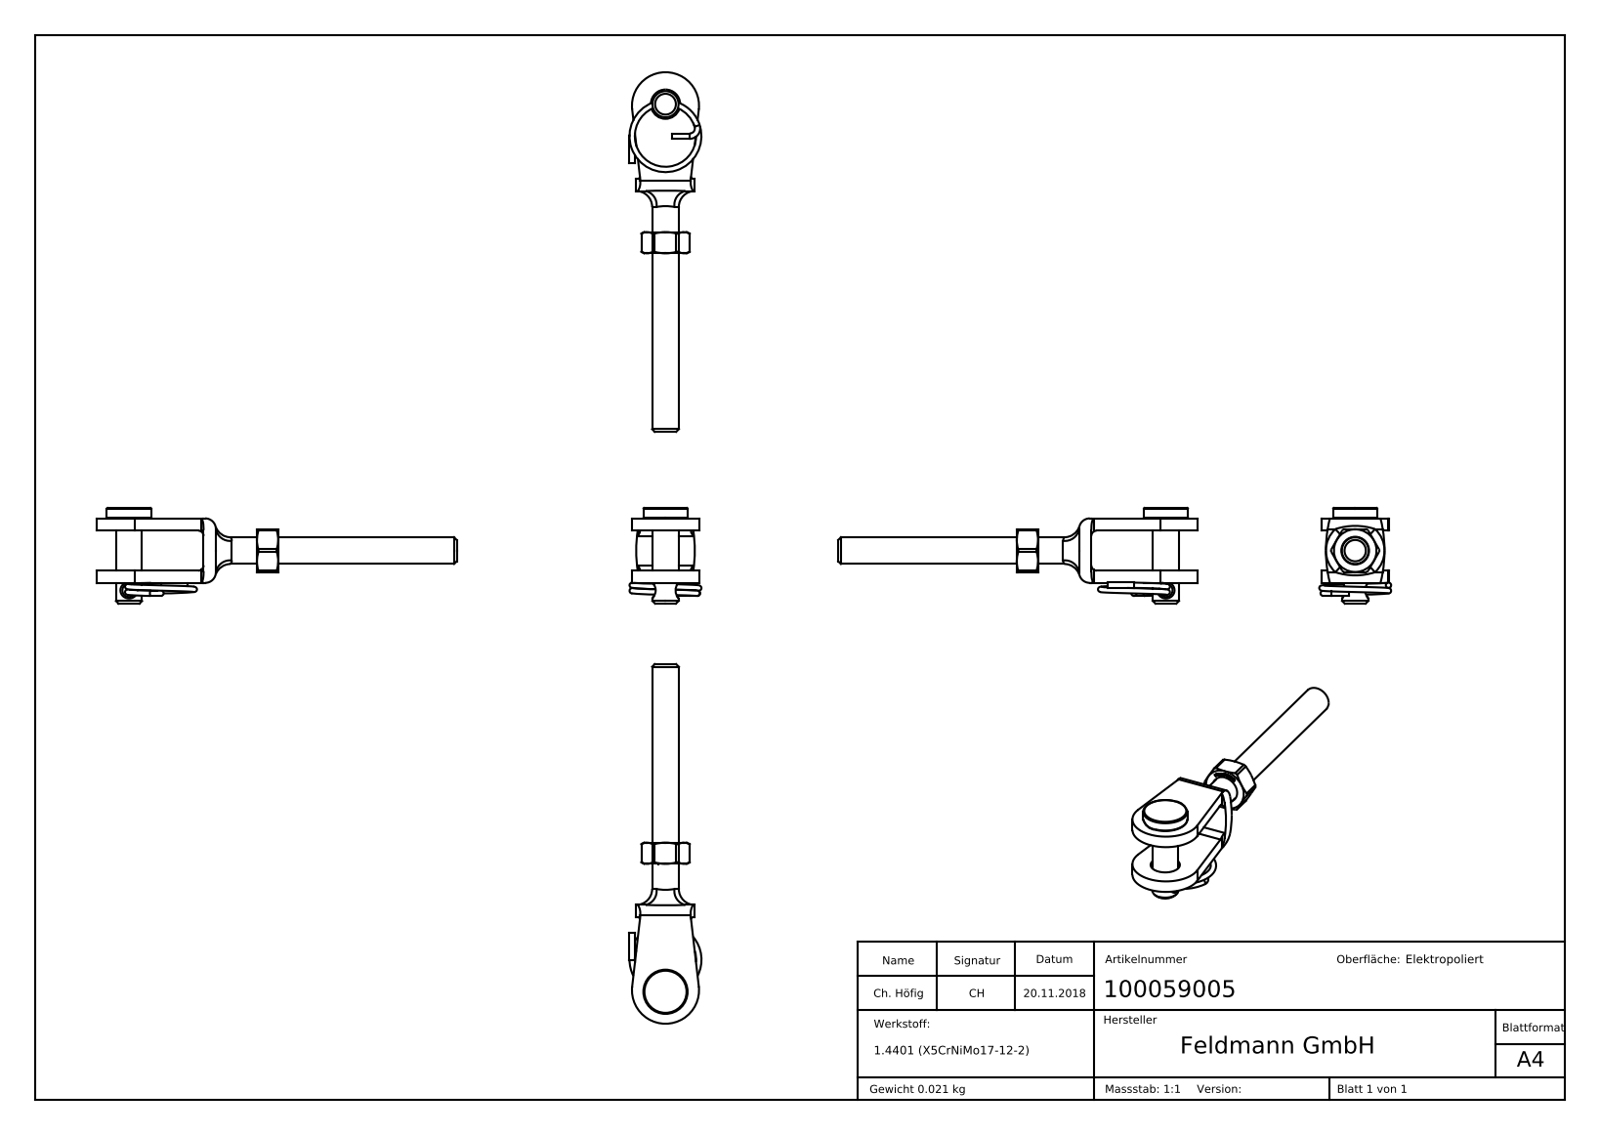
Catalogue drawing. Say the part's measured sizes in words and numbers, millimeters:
The part is named "10005900X Teil1_100059005 Teil1; 10005900X Teil2; 100059005; 10005900X Teil1 (+5 more)". Its 3-D file was written by "SolidWorks 2018 (CONFIG_CONTROL_DESIGN)". It is 4 solids with 299 faces: 128 planar, 27 cylindrical and 144 other. Overall it measures 67.5 by 18 by 13.5 millimeters. Its volume is 2 675 cubic millimeters and its surface area 2 901 square millimeters. Round holes: 1 of diameter 2.5, 1 of diameter 4.2, 1 of diameter 5.5. Round bosses or shafts: 2 of diameter 1, 1 of diameter 8.3, 1 of diameter 5, 1 of diameter 4.9. Partial cylindrical surfaces (rounded edges, fillets, slot ends): 6 of radius 0.5, 2 of radius 0.4, 2 of radius 1, 2 of radius 2, 2 of radius 24.78, 1 of radius 6.29. The main face-to-face distances are 2.3, 9.8, 12.1, 7.5, 2, 4.3, 14.1, 11.8, 8, 2.05.
